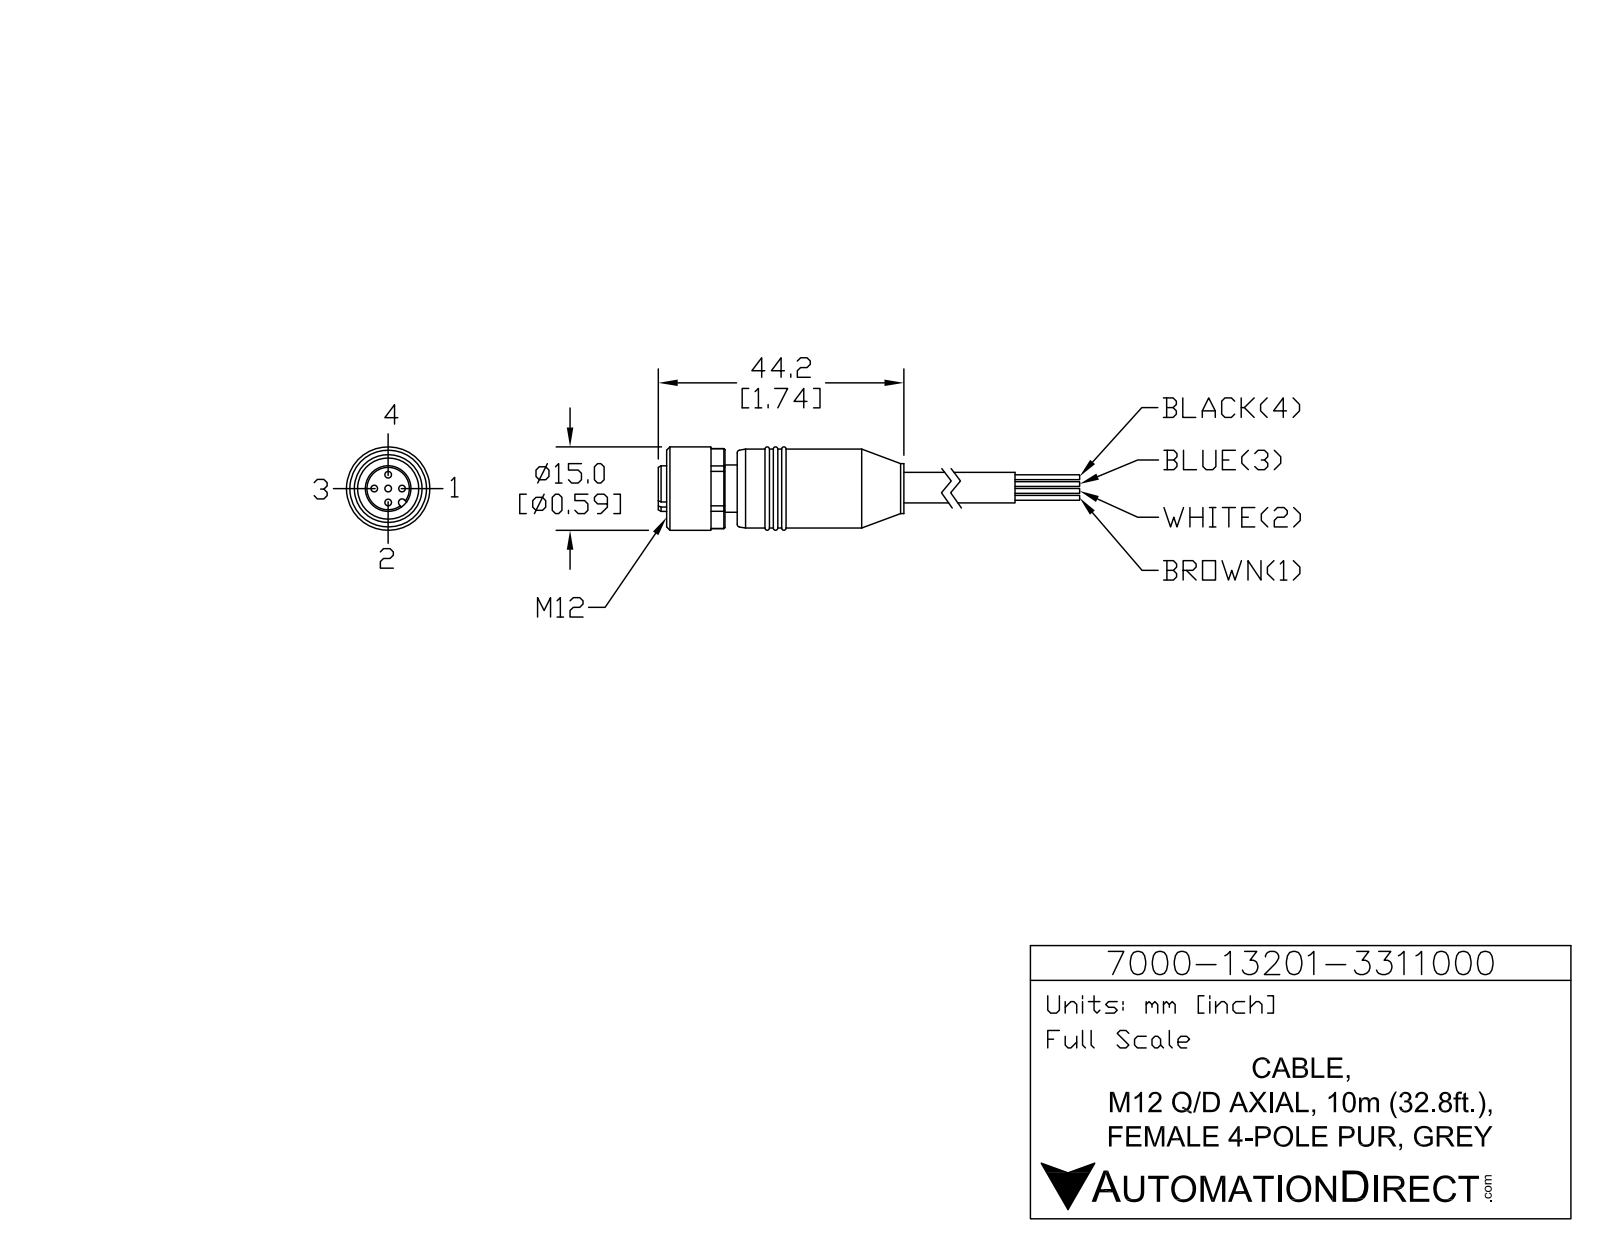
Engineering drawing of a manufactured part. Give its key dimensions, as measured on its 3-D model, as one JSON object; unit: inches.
{"part_name": "7000-13201-3311000", "step_written_by": "SolidWorks 2015 (AUTOMOTIVE_DESIGN)", "units": "inches", "bodies": {"solids": 1, "faces": 94, "planar": 28, "cylindrical": 38, "other": 28}, "overall_size": [2.528, 0.591, 0.591], "volume_in3": 0.404, "surface_area_in2": 5.191, "round_holes": [[0.047, 5], [0.433, 1]], "round_bosses_or_shafts": [[0.591, 1], [0.559, 1], [0.354, 1], [0.335, 1], [0.323, 1], [0.256, 1]], "partial_cylinders_radius": [[0.026, 1], [0.283, 1]], "face_to_face_distances": [0.087, 0.512, 0.118, 0.205, 0.354, 0.472, 0.559, 2.528, 2.173, 2.055], "hole_center_spacings": [0.098, 0.139, 0.197]}
